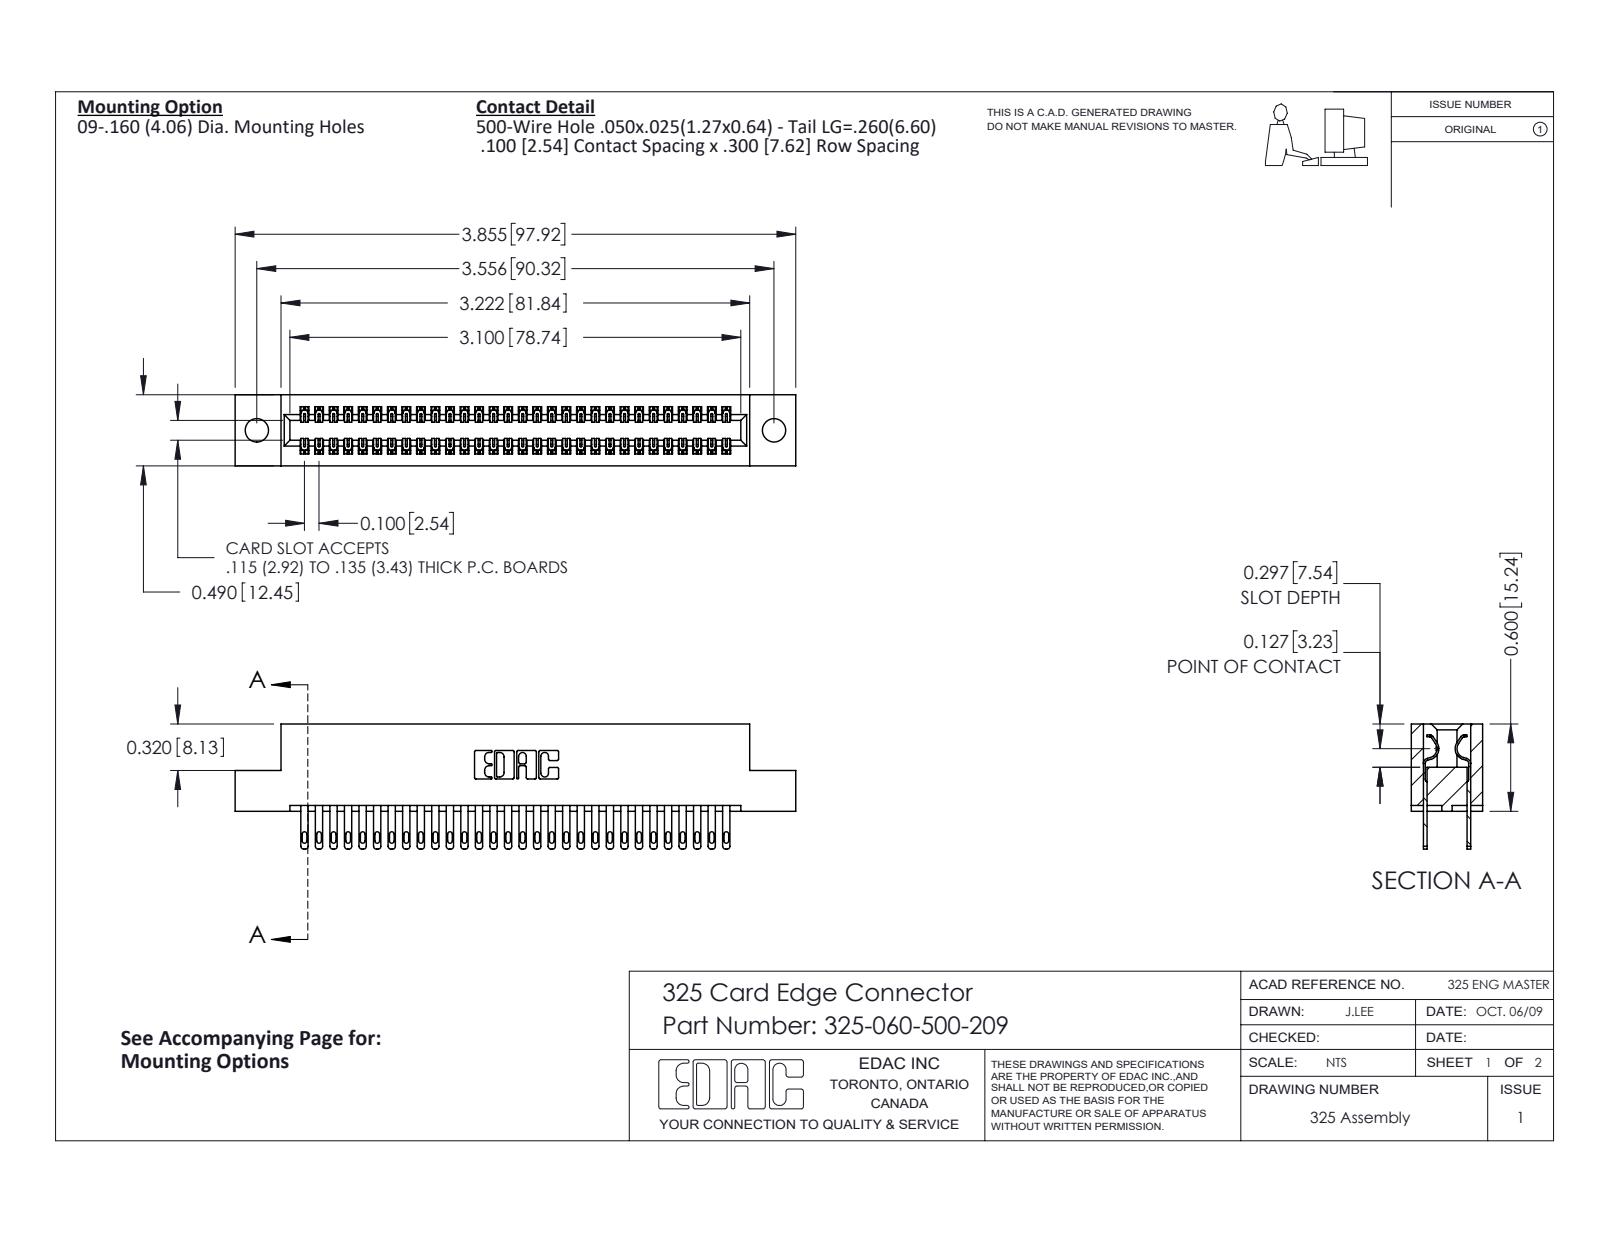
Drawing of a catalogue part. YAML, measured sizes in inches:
part_name: "325 Part_.160 TH; 325-292-001_325-293-100; 325-060-500-209"
step_written_by: "SolidWorks 2016 (CONFIG_CONTROL_DESIGN)"
units: inches
bodies: {solids: 61, faces: 2994, planar: 1870, cylindrical: 1124, other: 0}
overall_size: [3.855, 0.86, 0.49]
volume: 0.762
surface_area: 23.83
round_holes:
  - {diameter: 0.16, count: 2}
partial_cylinders:
  - {radius: 0.006, count: 90}
  - {radius: 0.016, count: 60}
  - {radius: 0.02, count: 60}
  - {radius: 0.01, count: 22}
  - {radius: 0.007, count: 6}
  - {radius: 0.031, count: 6}
  - {radius: 0.026, count: 3}
  - {radius: 0.014, count: 2}
face_to_face_distances: [0.083, 0.407, 0.3, 0.107, 0.383, 0.025, 0.49, 0.325, 0.275, 0.04]
hole_center_spacings: [3.556]
